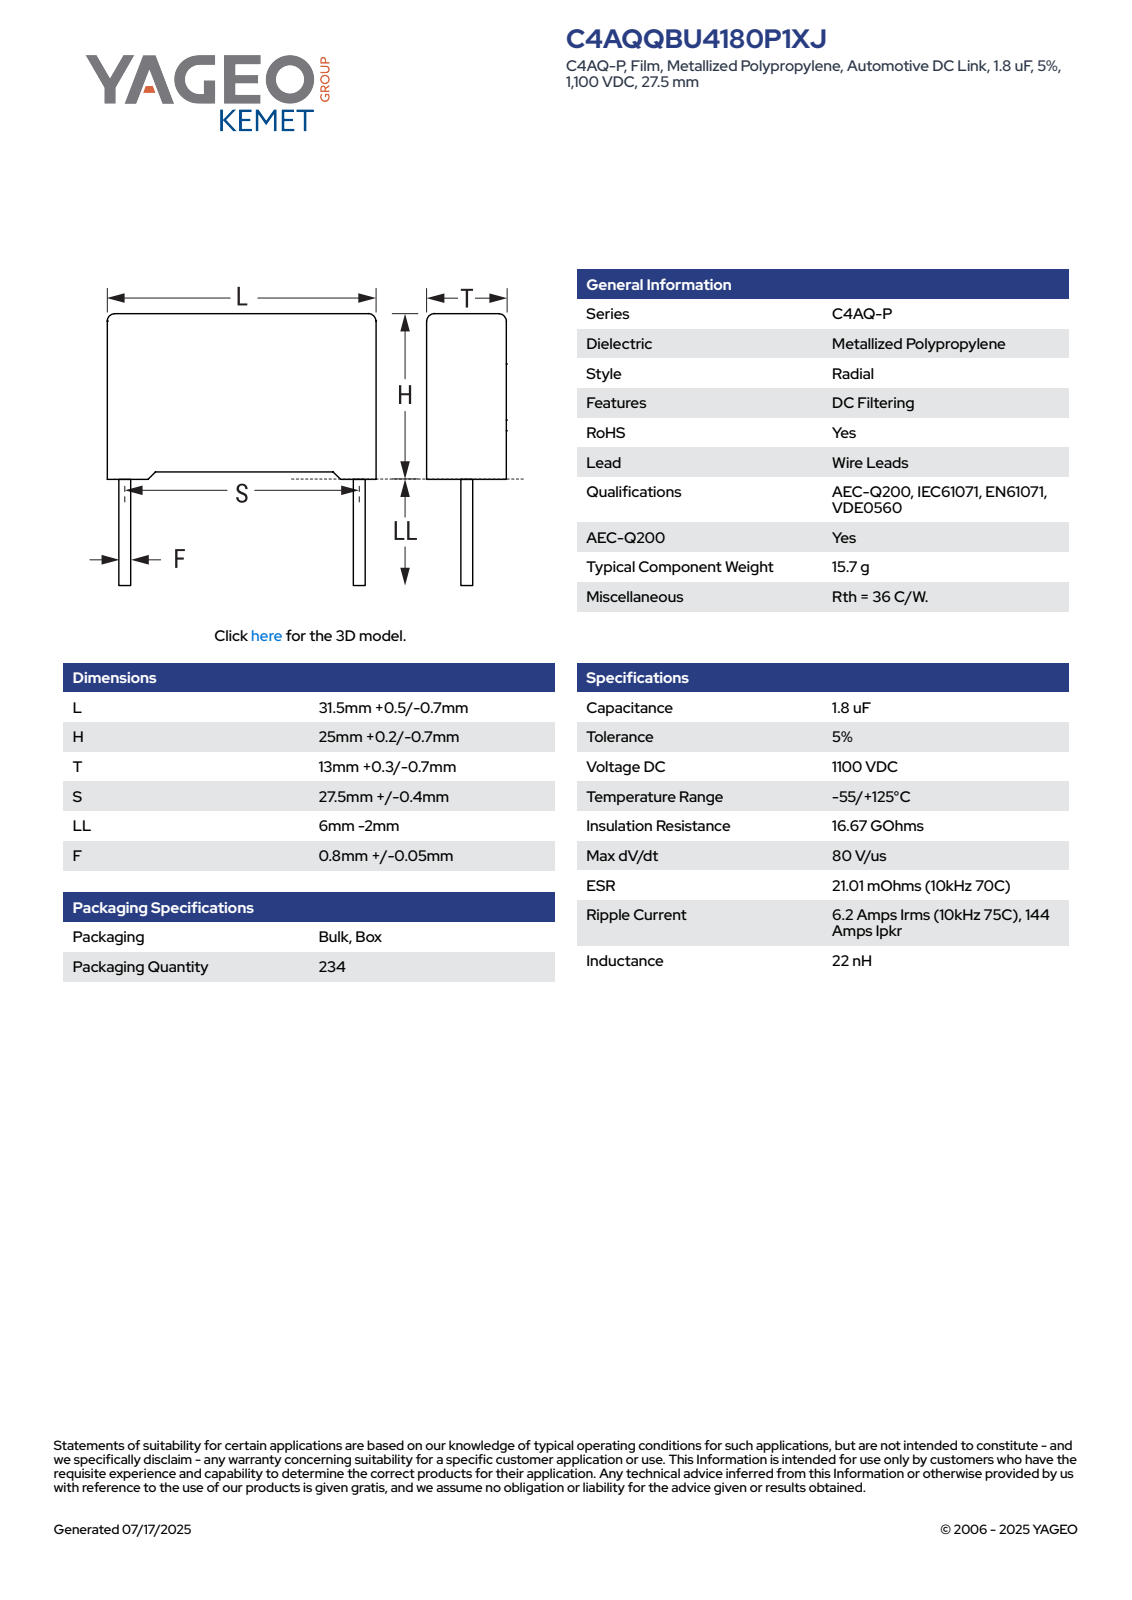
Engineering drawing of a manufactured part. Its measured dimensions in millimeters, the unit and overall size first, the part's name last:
Units: millimetres
Overall size (bounding box): 32 × 29.2 × 13.3
Round bosses / shafts (diameter × count): ⌀0.85 ×2
Partial cylindrical surfaces — rounded edges, fillets, slot ends (radius × count): R0.5 ×4
Main face-to-face distances: 13.3, 32, 24.33, 24.45, 0.87, 0.75, 25.2, 1.07, 13.31, 30.93
Volume: 10 402 mm³ · Surface area: 3 204 mm²
Bodies: 4 solids, 85 faces (77 planar, 8 cylindrical, 0 other)
Part name (STEP PRODUCT): CFR_RB2CFP_31.5X25X13_L32H25.2T13.3S27.5LL4F0.85
STEP written by: SolidWorks 2014 (AUTOMOTIVE_DESIGN)
